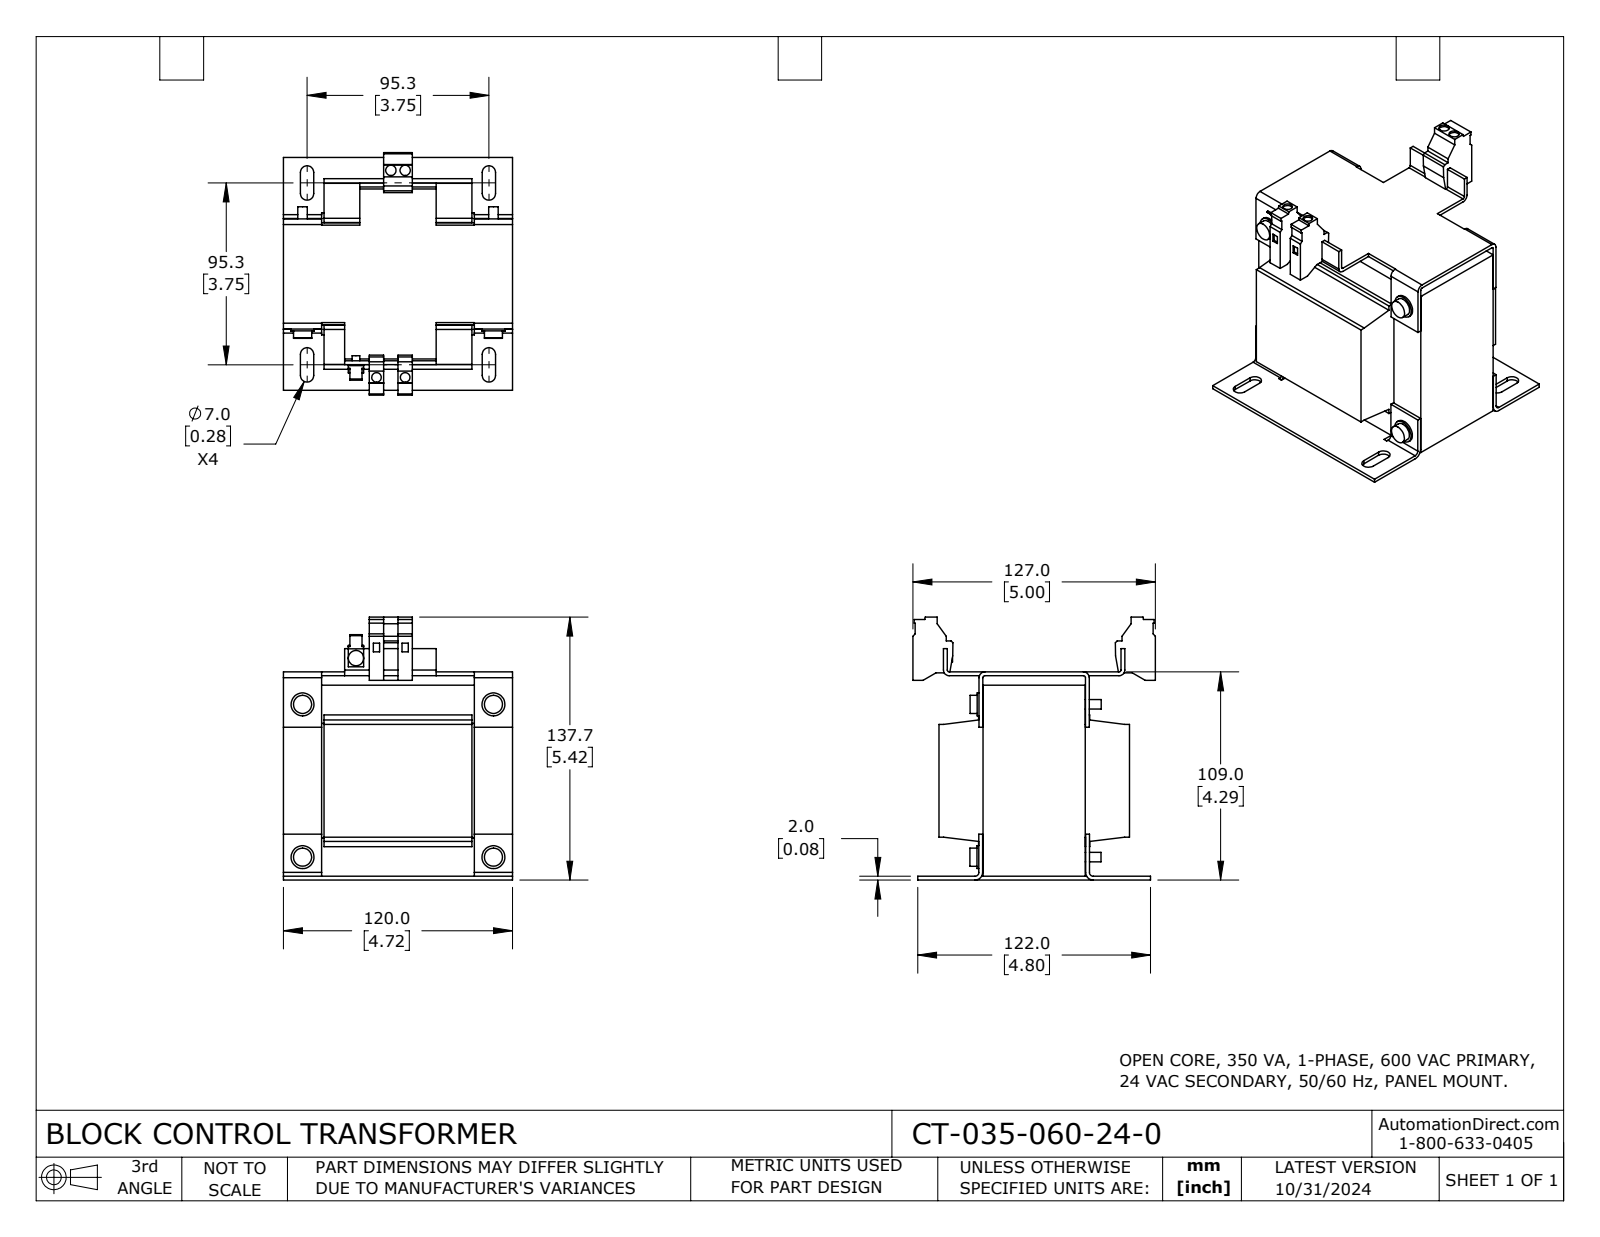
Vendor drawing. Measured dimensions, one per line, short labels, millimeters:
name: CT-035-060-24-0
written by: SolidWorks 2023 (CONFIG_CONTROL_DESIGN)
unit: mm
bodies: 1 solid, 322 faces (237 planar, 85 cylindrical, 0 other)
size: 137.7 × 127 × 120
volume: 921 100 mm³; area: 134 800 mm²
holes: 2× ⌀5, 2× ⌀5.4
bosses: 4× ⌀12, 4× ⌀9.5, 4× ⌀6, 4× ⌀5, 1× ⌀8, 1× ⌀4
rounds: 8× R3.5, 4× R1, 4× R3, 2× R2, 2× R4
face distances: 2, 107, 100, 20, 21.3, 98.8, 23.1, 76.7, 78.7, 80
hole spacings: 108.7, 7.5, 15, 108.4, 109.4
